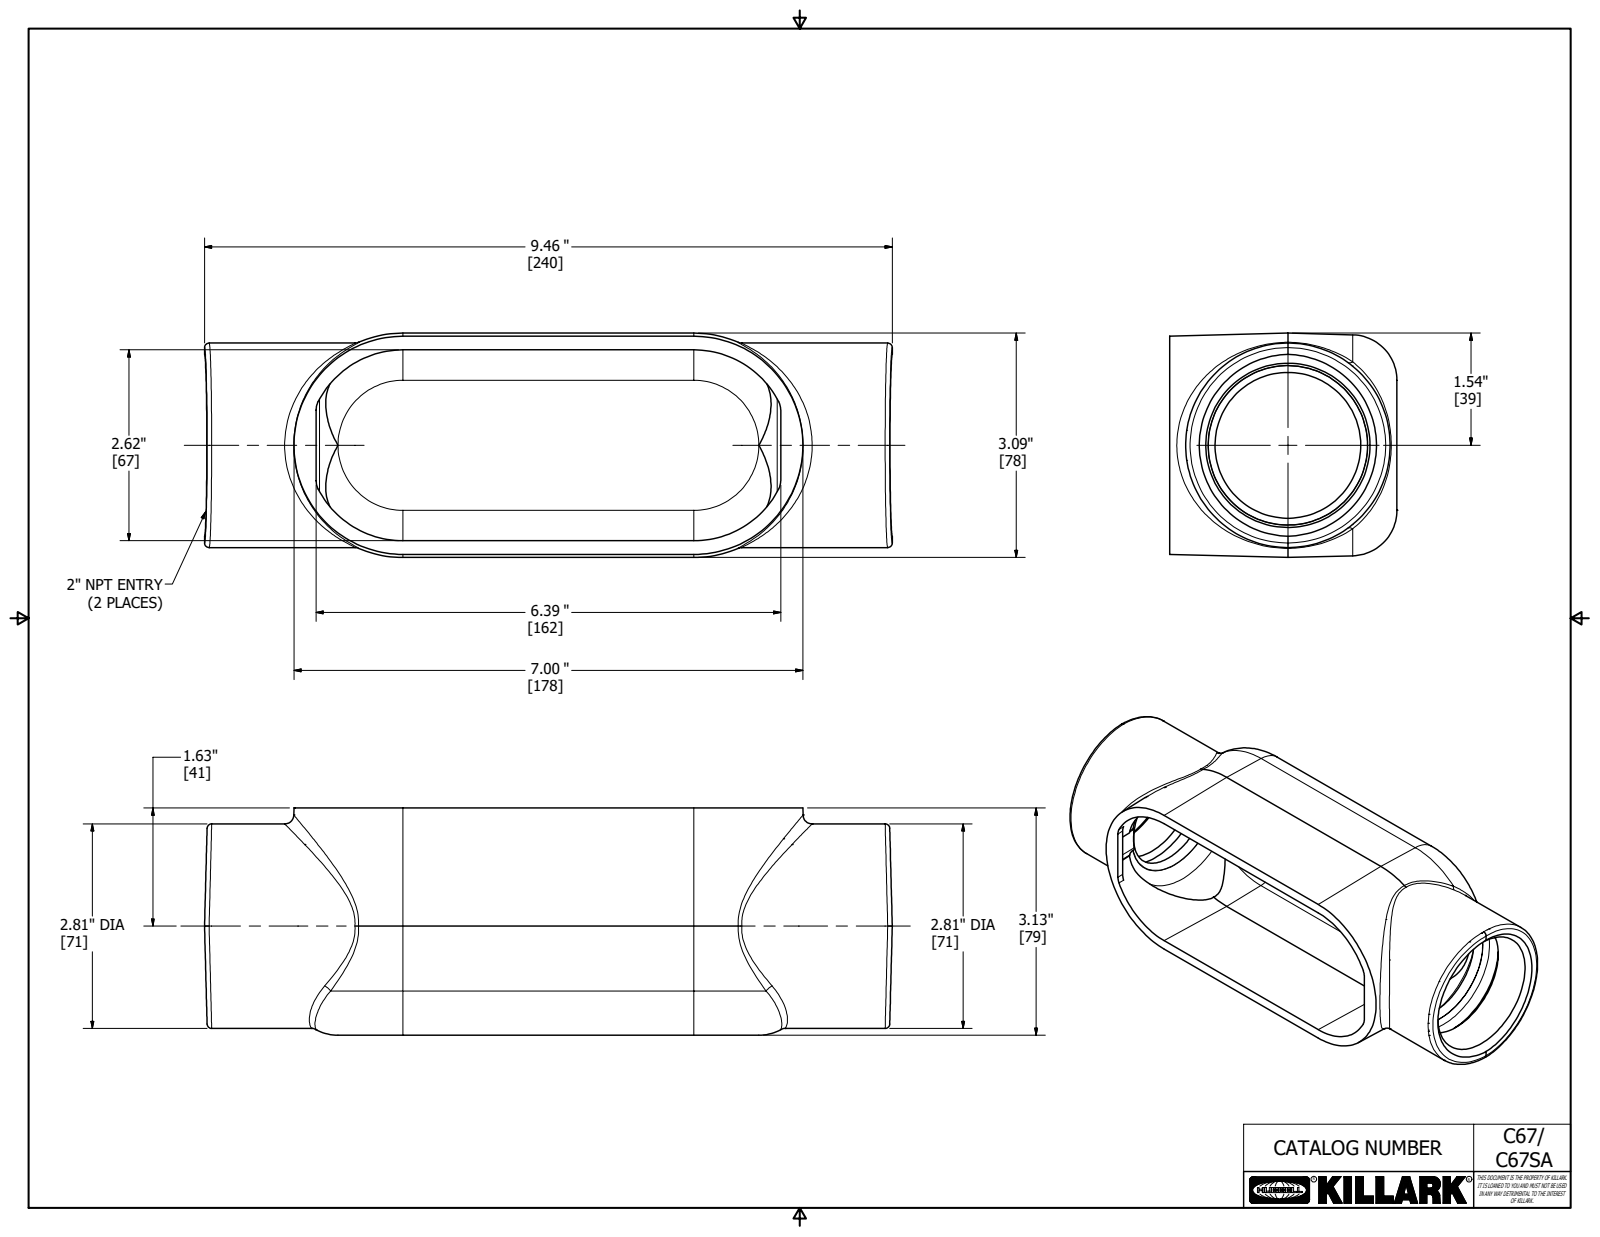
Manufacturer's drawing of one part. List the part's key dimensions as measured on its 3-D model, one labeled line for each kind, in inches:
Part name (STEP PRODUCT): 17707
STEP written by: Autodesk Inventor 2018 (AUTOMOTIVE_DESIGN)
Units: inches
Bodies: 1 solid, 100 faces (34 planar, 18 cylindrical, 48 other)
Overall size (bounding box): 9.46 × 3.125 × 3.085
Volume: 16.39 in³ · Surface area: 170.1 in²
Round holes (diameter × count): ⌀2.381 ×1, ⌀2.625 ×1
Round bosses / shafts (diameter × count): ⌀2.812 ×1
Partial cylindrical surfaces — rounded edges, fillets, slot ends (radius × count): R0.05 ×4, R0.125 ×4, R0.437 ×2, R0.625 ×2
Main face-to-face distances: 0.187, 2.898, 3.085, 2.71, 3.125, 2.937, 9.46, 0.031, 0.156, 3.094
